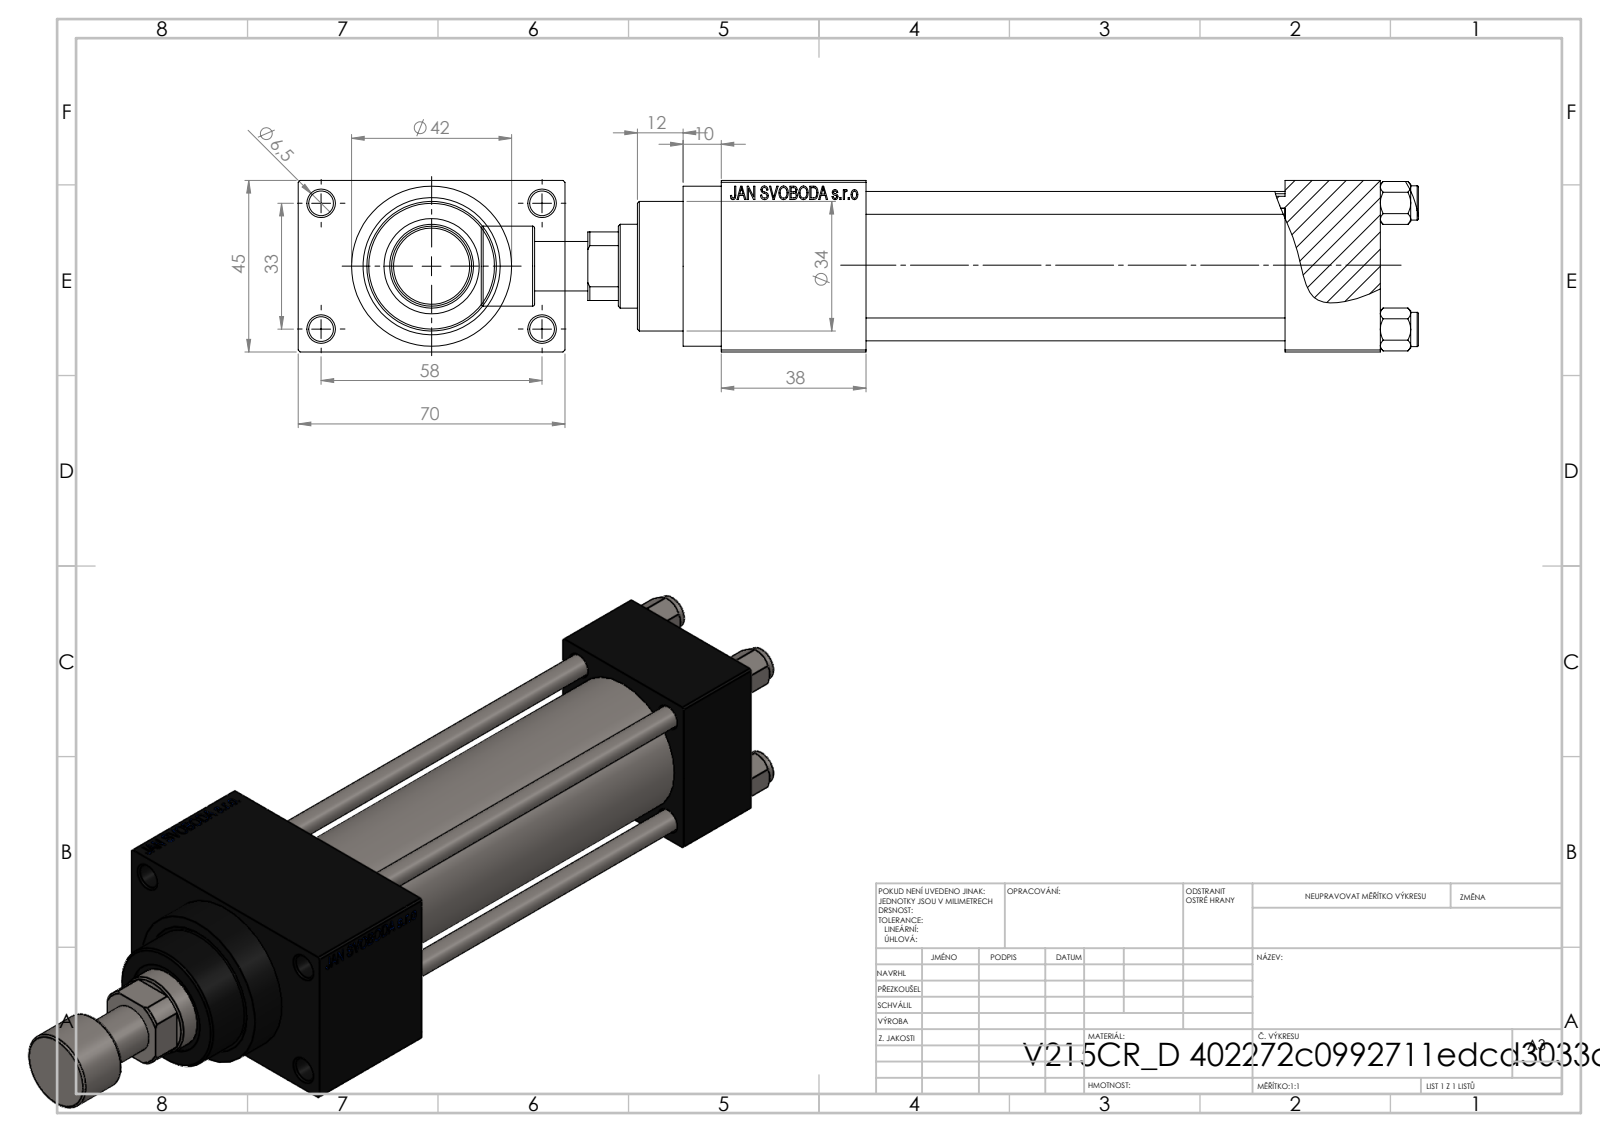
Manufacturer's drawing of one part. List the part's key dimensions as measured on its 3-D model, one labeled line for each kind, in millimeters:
Part name (STEP PRODUCT): NUT_M5_D; V215CR_D_Body; V215CR_D_TYCINKA; V215CR_VCP_D (+2 more)
STEP written by: SolidWorks 2019 (CONFIG_CONTROL_DESIGN)
Units: millimetres
Bodies: 12 solids, 1115 faces (499 planar, 92 cylindrical, 524 other)
Overall size (bounding box): 246 × 70 × 45
Volume: 298 962 mm³ · Surface area: 103 909 mm²
Round holes (diameter × count): ⌀6 ×4, ⌀6.5 ×4, ⌀7 ×2, ⌀13.16 ×2, ⌀20 ×2, ⌀10.5 ×1, ⌀22 ×1, ⌀24 ×1, ⌀25 ×1, ⌀32 ×1, ⌀33 ×1
Round bosses / shafts (diameter × count): ⌀9 ×4, ⌀42 ×1, ⌀38 ×1, ⌀34 ×1, ⌀21 ×1, ⌀13 ×1
Main face-to-face distances: 45, 25, 12.5, 110, 135, 57.5, 148, 38, 173, 70
Hole centre spacings: 12.4, 23.48, 33.2, 33.37, 35.35, 45.6, 56.35, 33
